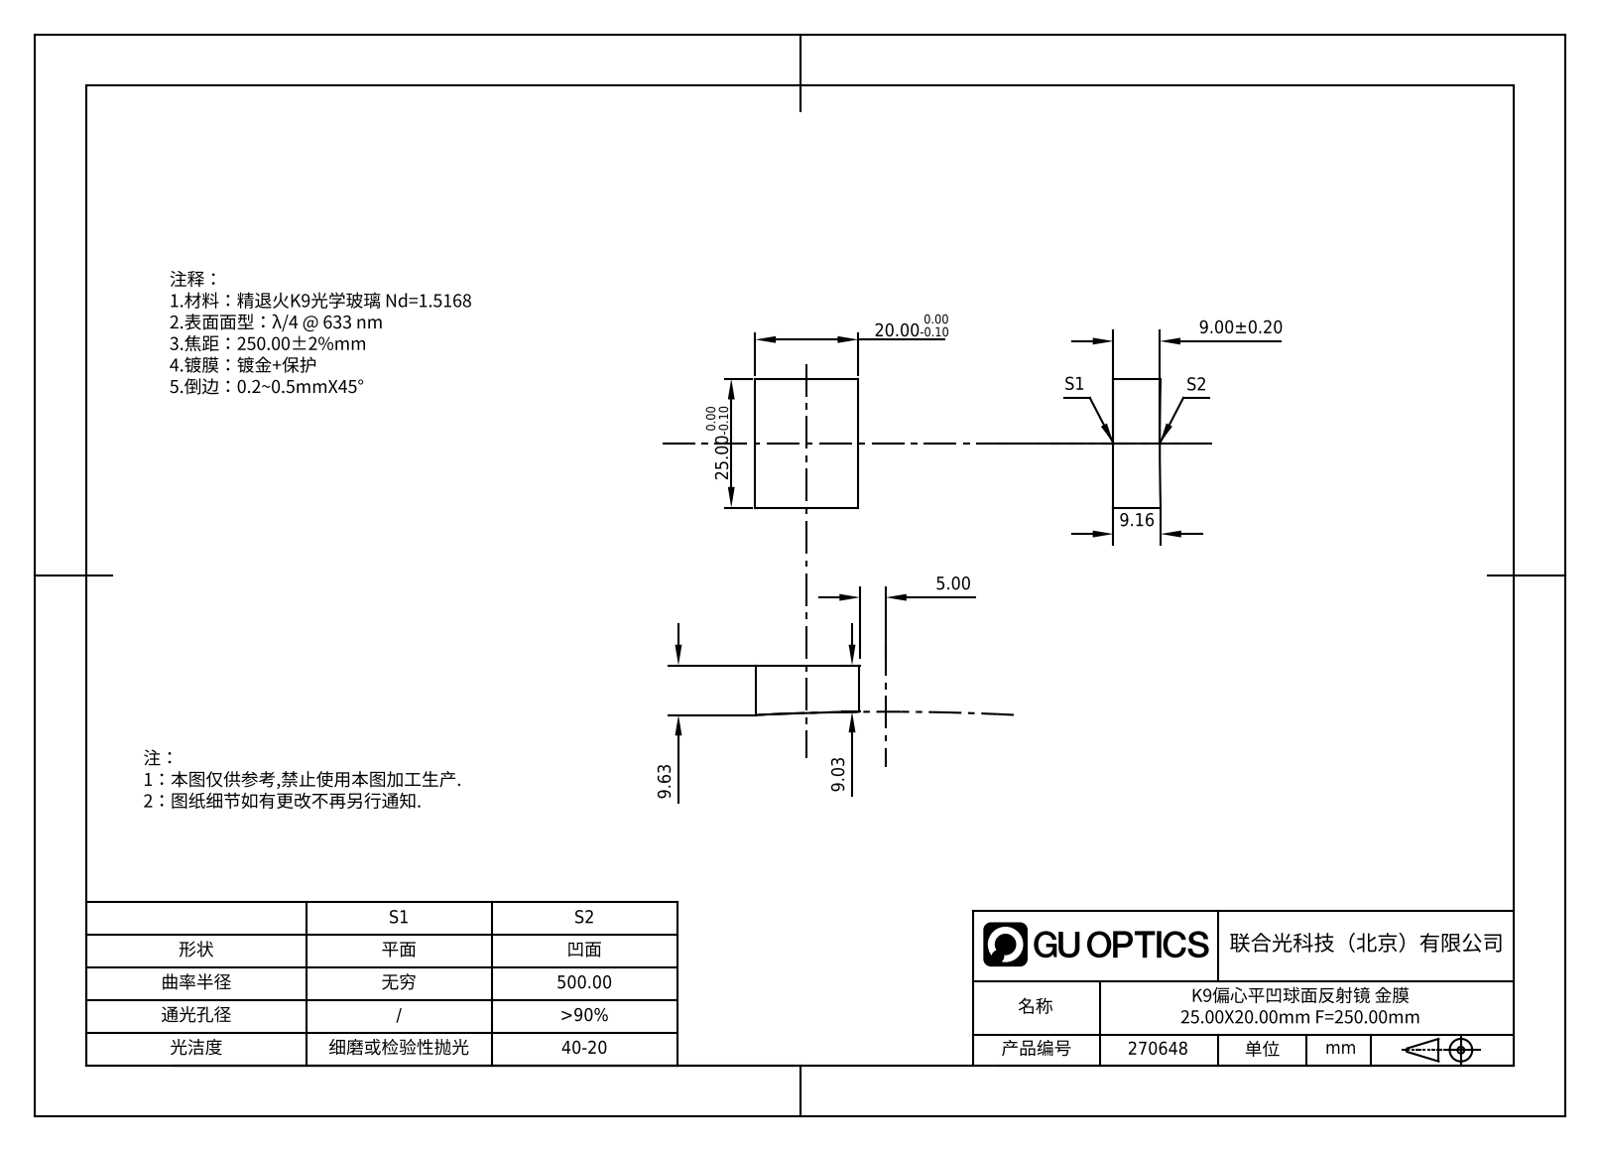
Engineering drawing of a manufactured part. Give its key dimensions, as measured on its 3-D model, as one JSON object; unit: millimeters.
{"part_name": "270648", "step_written_by": "SolidWorks 2020 (CONFIG_CONTROL_DESIGN)", "units": "millimeters", "bodies": {"solids": 1, "faces": 7, "planar": 5, "cylindrical": 0, "other": 2}, "overall_size": [25, 20, 9.78], "volume_mm3": 4655, "surface_area_mm2": 1846, "face_to_face_distances": [20, 25]}
